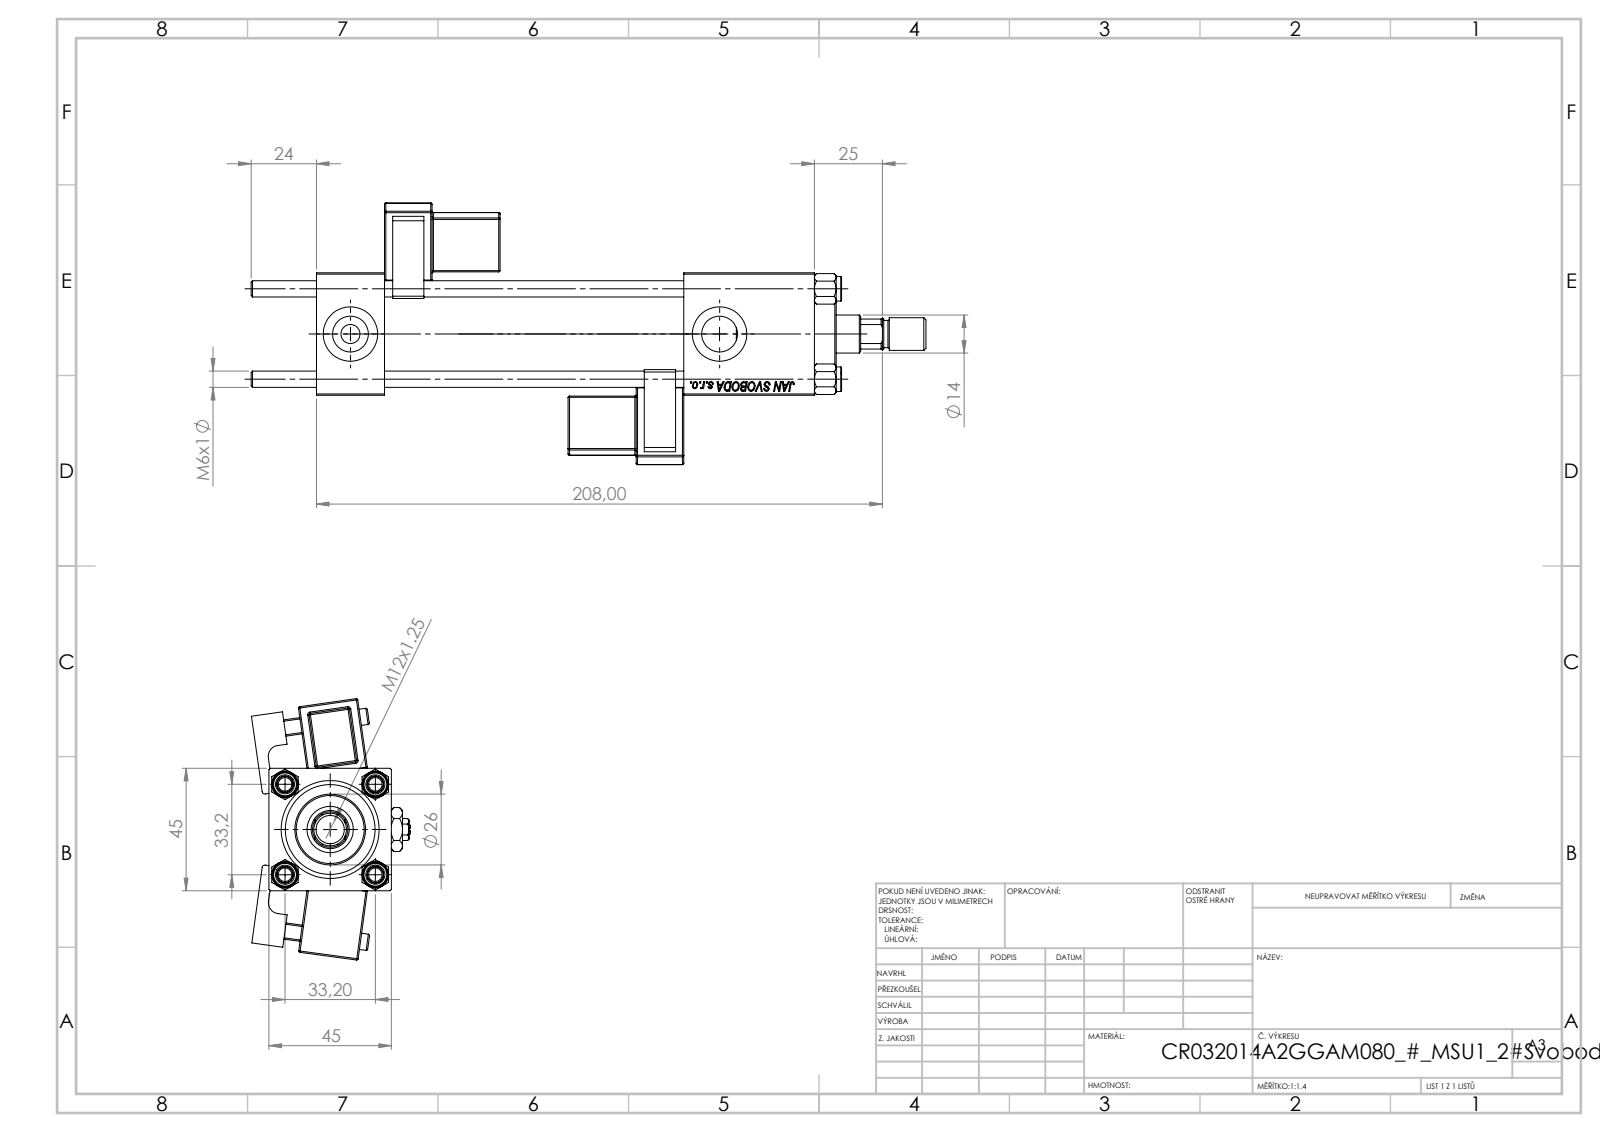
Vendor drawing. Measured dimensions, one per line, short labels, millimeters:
name: NUT_M5; V215_VC_A; V215CR_VCP; CR025_012_A_0_G_A_G_M_020_+#_##_TYCINKA (+4 more)
written by: SolidWorks 2019 (CONFIG_CONTROL_DESIGN)
unit: mm
bodies: 15 solids, 1356 faces (606 planar, 150 cylindrical, 600 other)
size: 248 × 96.03 × 58.41
volume: 275 292 mm³; area: 107 154 mm²
holes: 4× ⌀6, 2× ⌀7, 2× ⌀13.16, 2× ⌀20, 1× ⌀6.5, 1× ⌀13, 1× ⌀14, 1× ⌀17, 1× ⌀24, 1× ⌀32, 1× ⌀33
bosses: 4× ⌀9, 2× ⌀6, 1× ⌀38, 1× ⌀26, 1× ⌀12, 1× ⌀10
rounds: 48× R0.5, 2× R1, 2× R2.5, 2× R4, 1× R6.5
face distances: 45, 25, 3, 135, 110, 183, 158, 48, 15, 92.5
hole spacings: 23.48, 33.2, 46.95, 135.66
